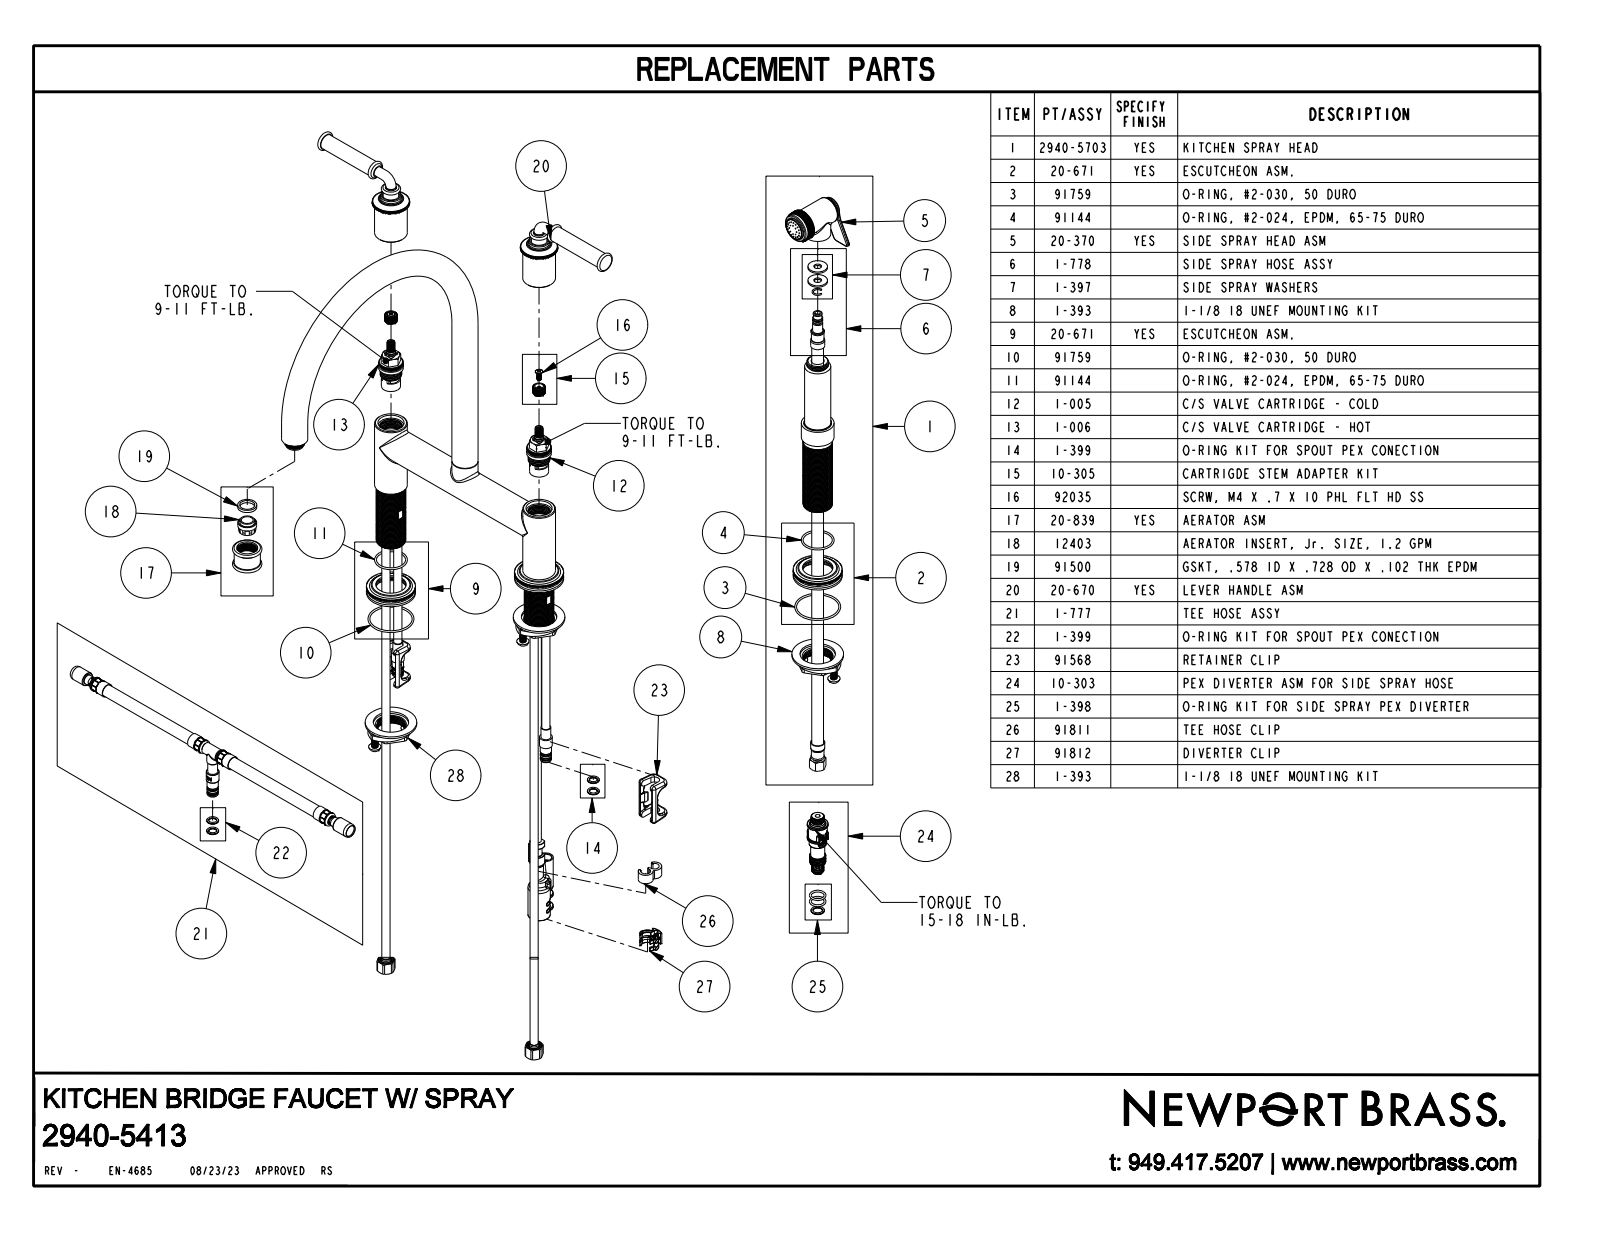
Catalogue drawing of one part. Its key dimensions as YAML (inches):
part_name: "2940-5413"
step_written_by: "CREO PARAMETRIC BY PTC INC, 2023134 (CONFIG_CONTROL_DESIGN)"
units: inches
bodies: {solids: 6, faces: 2524, planar: 1454, cylindrical: 831, other: 239}
overall_size: [18.543, 15.006, 11.152]
volume: 47.13
surface_area: 214.6
round_holes:
  - {diameter: 0.65, count: 2}
  - {diameter: 0.06, count: 1}
  - {diameter: 0.231, count: 1}
  - {diameter: 0.41, count: 1}
  - {diameter: 0.525, count: 1}
  - {diameter: 0.56, count: 1}
  - {diameter: 0.62, count: 1}
  - {diameter: 0.691, count: 1}
  - {diameter: 0.812, count: 1}
  - {diameter: 0.835, count: 1}
  - {diameter: 0.886, count: 1}
  - {diameter: 0.93, count: 1}
round_bosses_or_shafts:
  - {diameter: 1.25, count: 4}
  - {diameter: 1.875, count: 3}
  - {diameter: 1.775, count: 3}
  - {diameter: 1, count: 3}
  - {diameter: 0.39, count: 3}
  - {diameter: 1.25, count: 2}
  - {diameter: 0.8, count: 2}
  - {diameter: 0.595, count: 2}
partial_cylinders:
  - {radius: 0.04, count: 10}
  - {radius: 0.07, count: 5}
  - {radius: 0.06, count: 4}
  - {radius: 0.156, count: 2}
  - {radius: 0.16, count: 2}
  - {radius: 0.34, count: 2}
  - {radius: 0.715, count: 2}
  - {radius: 0.187, count: 1}
face_to_face_distances: [0.31, 0.38, 0.07, 0.23, 4.692, 0.131, 0.15, 0.08, 4.462, 4.382]
hole_center_spacings: [4, 10.032, 1.389, 8, 9.2]
